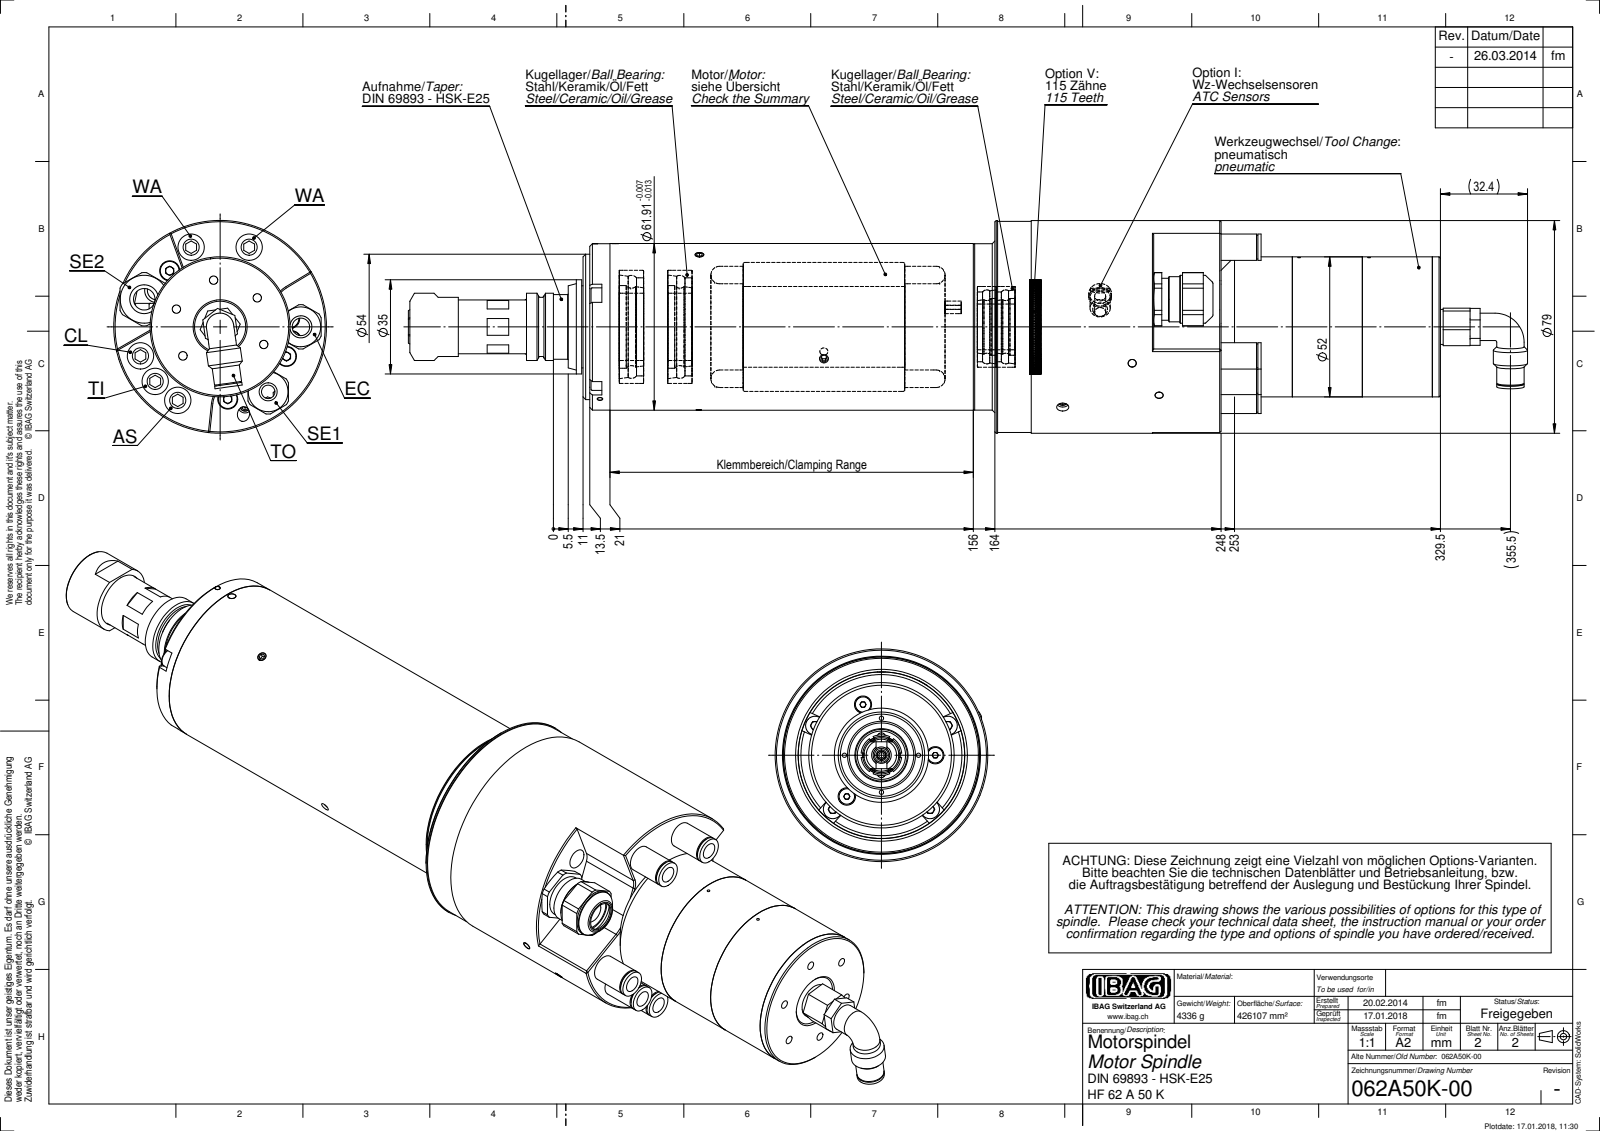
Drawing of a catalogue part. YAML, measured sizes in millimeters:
part_name: "062A50K-00"
step_written_by: "SolidWorks 2014 (CONFIG_CONTROL_DESIGN)"
units: millimeters
bodies: {solids: 0, faces: 624, planar: 244, cylindrical: 228, other: 152}
overall_size: [415.71, 79, 79]
round_holes:
  - {diameter: 3.1, count: 6}
  - {diameter: 6, count: 6}
  - {diameter: 1.6, count: 4}
  - {diameter: 4.5, count: 4}
  - {diameter: 7.4, count: 3}
  - {diameter: 13, count: 3}
  - {diameter: 1, count: 2}
  - {diameter: 3.3, count: 2}
  - {diameter: 3, count: 1}
  - {diameter: 5, count: 1}
  - {diameter: 6.5, count: 1}
  - {diameter: 6.7, count: 1}
round_bosses_or_shafts:
  - {diameter: 9.8, count: 5}
  - {diameter: 7, count: 4}
  - {diameter: 5.7, count: 3}
  - {diameter: 14.8, count: 2}
  - {diameter: 13.79, count: 2}
  - {diameter: 12.59, count: 2}
  - {diameter: 10.16, count: 2}
  - {diameter: 79, count: 1}
partial_cylinders:
  - {radius: 3.7, count: 4}
  - {radius: 8.25, count: 2}
  - {radius: 9, count: 2}
  - {radius: 3, count: 1}
  - {radius: 9.9, count: 1}
  - {radius: 11, count: 1}
  - {radius: 21, count: 1}
face_to_face_distances: [2.5, 234.5, 316, 81.5, 150.5, 308.5, 10, 84, 165.5, 7.5]
hole_center_spacings: [17.5, 31.5, 13.75, 17.51, 19.45, 30.31, 19.16, 26]
